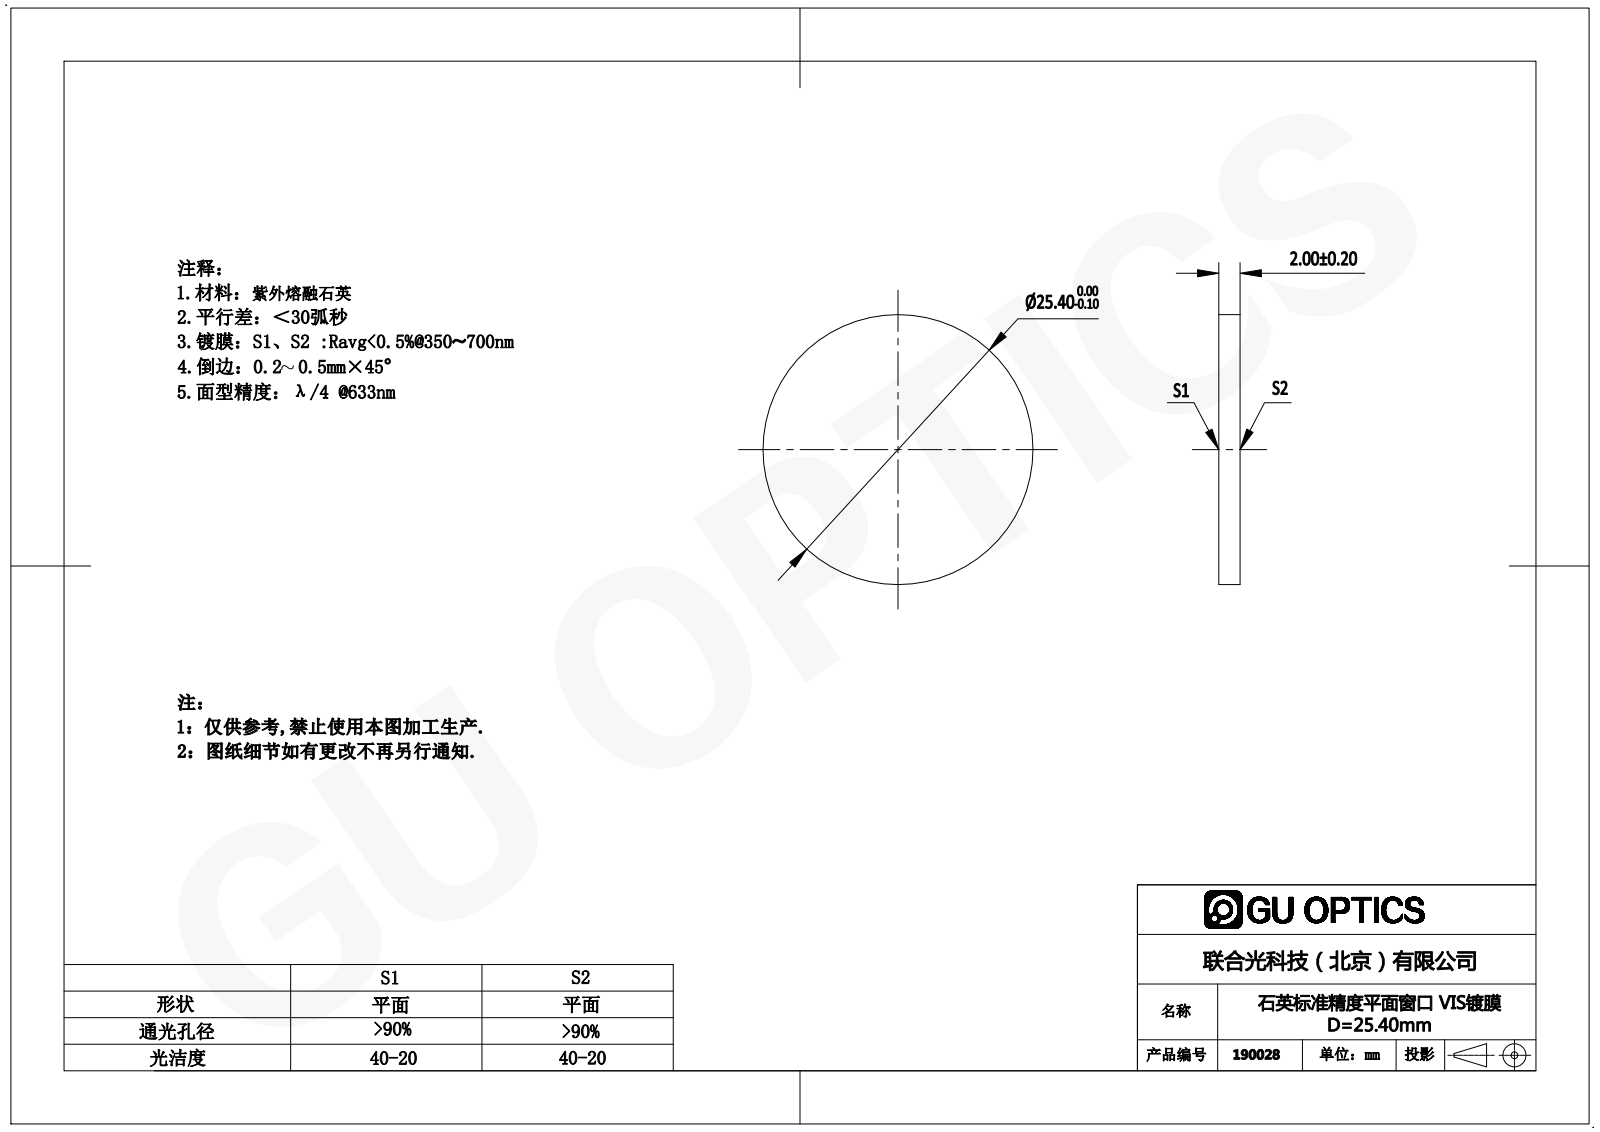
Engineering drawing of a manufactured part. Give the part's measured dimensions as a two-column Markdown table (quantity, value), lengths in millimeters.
| quantity | value |
| --- | --- |
| part name | 190006 |
| STEP written by | SolidWorks 2016 (AUTOMOTIVE_DESIGN) |
| units | millimeters |
| bodies | 1 solid, 4 faces (2 planar, 2 cylindrical, 0 other) |
| overall size | 25.4 × 25.4 × 2 |
| volume | 1 013 mm³ |
| surface area | 1 173 mm² |
| round bosses / shafts (diameter × count) | 25.4 × 1 |
| main face-to-face distances | 2 |
